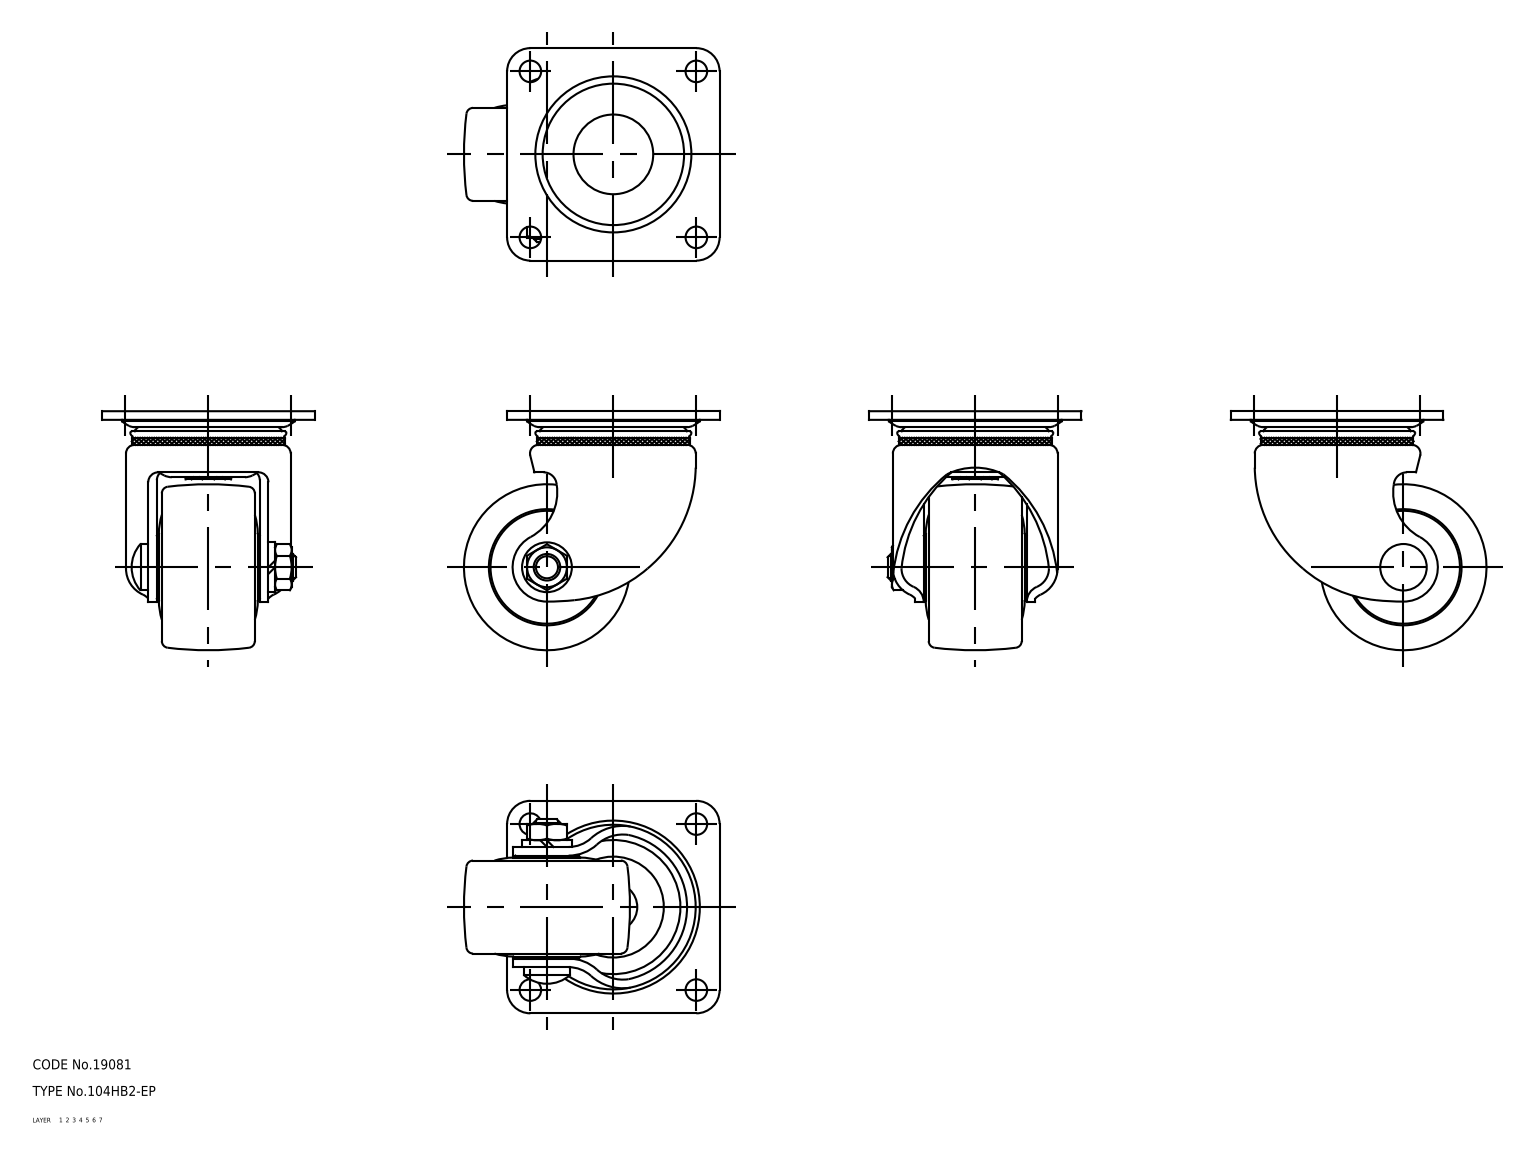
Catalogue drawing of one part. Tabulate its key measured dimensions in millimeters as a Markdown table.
| quantity | value |
| --- | --- |
| part name | wheel; mounting plate; main shaft; axle (+1 more) |
| STEP written by | CADfix (AUTOMOTIVE_DESIGN) |
| units | millimeters |
| bodies | 5 solids, 264 faces (0 planar, 0 cylindrical, 264 other) |
| overall size | 77 × 72 × 64 |
| volume | 99 063 mm³ |
| surface area | 37 374 mm² |
